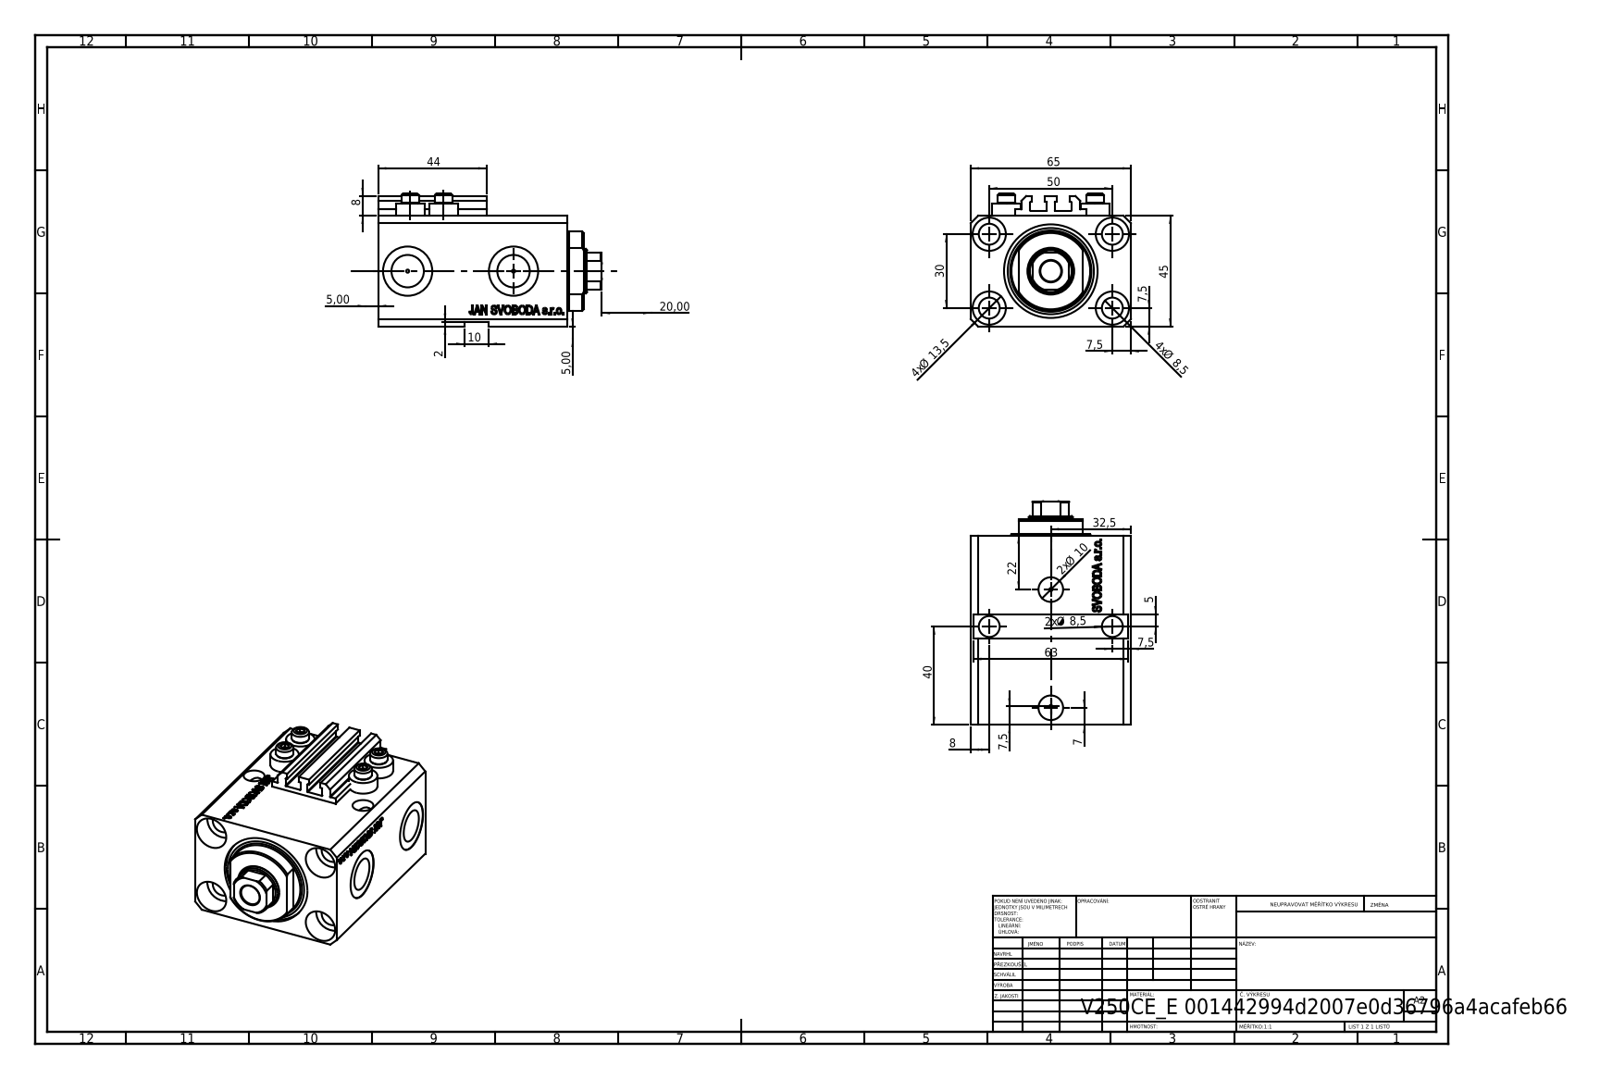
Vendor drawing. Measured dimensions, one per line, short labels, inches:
name: ALLEN BOLT V250CE; V250CE_C_VCP; V250CE_VC_E; V250CE_E_Body
written by: SolidWorks 2019 (CONFIG_CONTROL_DESIGN)
unit: in
bodies: 8 solids, 1083 faces (515 planar, 138 cylindrical, 430 other)
size: 3.579 × 2.559 × 2.126
volume: 11.97 in³; area: 96.72 in²
holes: 7× ⌀0.335, 4× ⌀0.049, 4× ⌀0.157, 4× ⌀0.531, 2× ⌀0.394, 2× ⌀0.518, 2× ⌀0.787, 1× ⌀0.709, 1× ⌀0.984, 1× ⌀1.496
bosses: 4× ⌀0.457, 4× ⌀0.276
rounds: 10× R0.008, 1× R0.335, 1× R0.63
face distances: 1.772, 2.559, 2.043, 3.031, 0.988, 0.079, 0.272, 2.76, 0.118, 0.354
hole spacings: 1.148, 1.969, 0.535, 0.595, 0.741, 0.747, 1.032, 1.048
